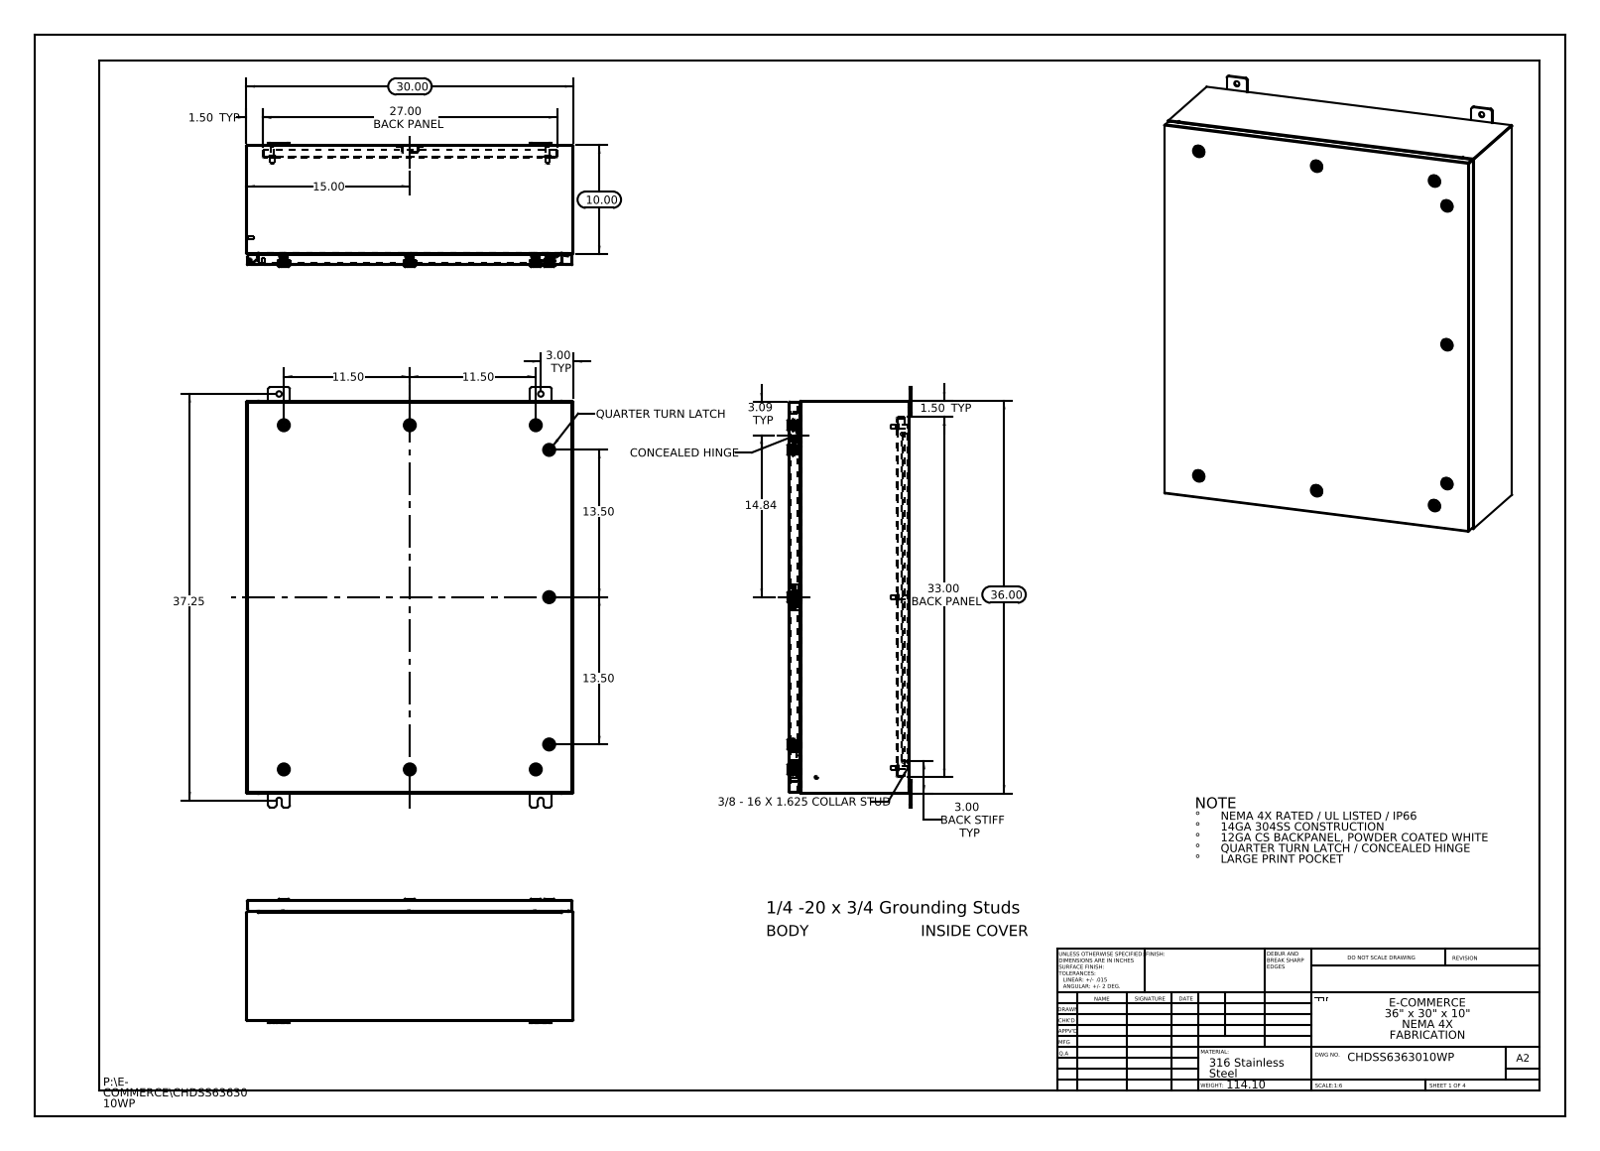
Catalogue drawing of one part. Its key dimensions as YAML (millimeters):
part_name: "Screw-221320-IB-Industrilas_Screw-221320-IB-Industrilas; CHDSS6363010WP Cover; CHDSS6363010WP Enclosure Stiffener; CHDSS6363010WP Body (+8 more)"
step_written_by: "SolidWorks 2013 (CONFIG_CONTROL_DESIGN)"
units: millimeters
bodies: {solids: 74, faces: 7912, planar: 2256, cylindrical: 2462, other: 3194}
overall_size: [977.9, 762, 288.4]
volume: 6627000
surface_area: 6475000
round_holes:
  - {diameter: 12.7, count: 10}
  - {diameter: 5, count: 9}
  - {diameter: 10, count: 9}
  - {diameter: 10.2, count: 9}
  - {diameter: 16, count: 9}
  - {diameter: 20, count: 9}
  - {diameter: 3.5, count: 2}
  - {diameter: 5.4, count: 1}
round_bosses_or_shafts:
  - {diameter: 6, count: 11}
  - {diameter: 28, count: 9}
  - {diameter: 19.8, count: 9}
  - {diameter: 15.9, count: 9}
  - {diameter: 15.5, count: 9}
  - {diameter: 13.5, count: 9}
  - {diameter: 10, count: 9}
  - {diameter: 2.9, count: 9}
partial_cylinders:
  - {radius: 0.2, count: 297}
  - {radius: 3, count: 297}
  - {radius: 0.7, count: 108}
  - {radius: 0.5, count: 36}
  - {radius: 5, count: 36}
  - {radius: 0.3, count: 26}
  - {radius: 4.8, count: 24}
  - {radius: 2.2, count: 22}
face_to_face_distances: [1.9, 1.9, 279.7, 277.7, 277.8, 275.9, 2.6, 25.4, 27.3, 250.5]
hole_center_spacings: [293.4, 396.9, 754.2, 853.4, 641.4, 801.4, 47.2, 54.1]
